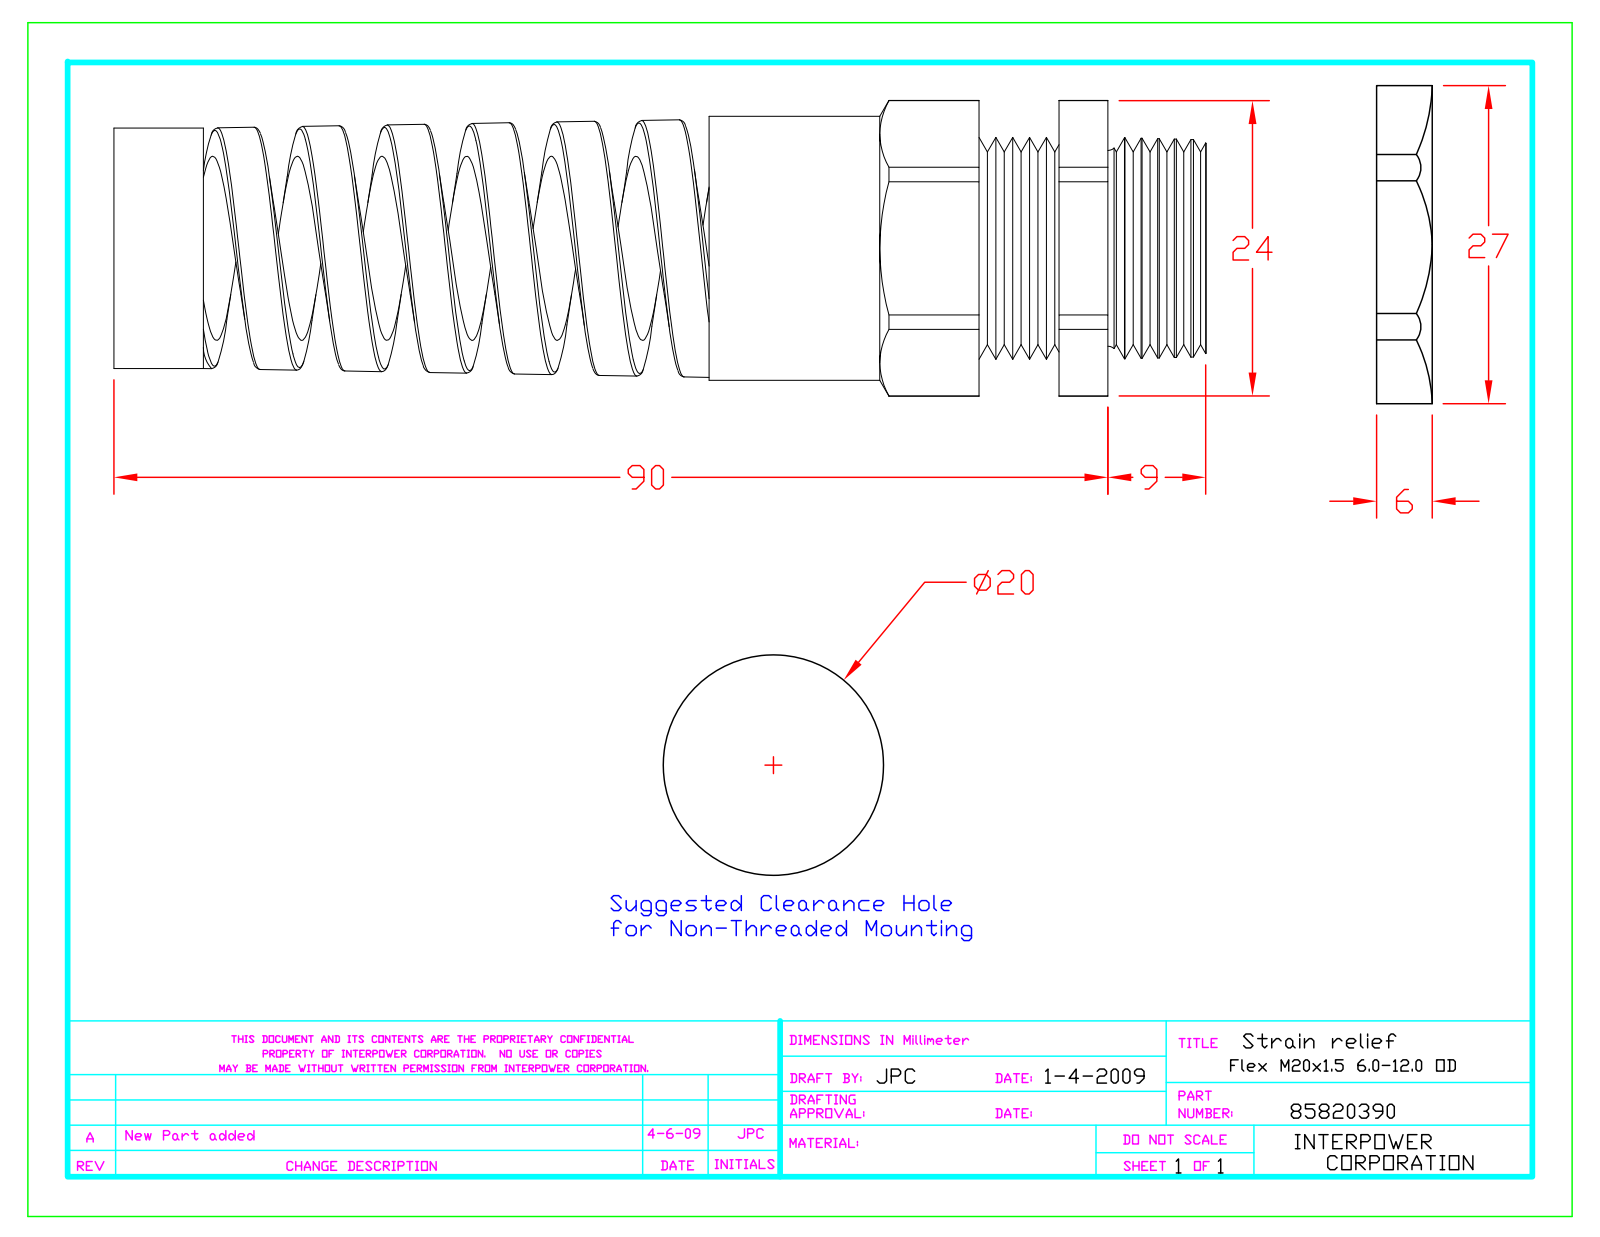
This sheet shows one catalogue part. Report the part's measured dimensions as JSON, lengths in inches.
{"part_name": "CF20MA", "step_written_by": "SolidWorks 2007 (CONFIG_CONTROL_DESIGN)", "units": "inches", "bodies": {"solids": 1, "faces": 139, "planar": 19, "cylindrical": 34, "other": 86}, "overall_size": [3.89, 1.053, 0.94], "volume_in3": 1.103, "surface_area_in2": 20.44, "round_holes": [[0.47, 1], [0.656, 1], [0.79, 1]], "round_bosses_or_shafts": [[0.94, 1], [0.856, 1]], "partial_cylinders_radius": [[0.526, 1]], "face_to_face_distances": [0.94, 0.961, 1.246, 0.285, 2.12, 3.081, 3.366, 3.54, 1.42, 0.459]}
